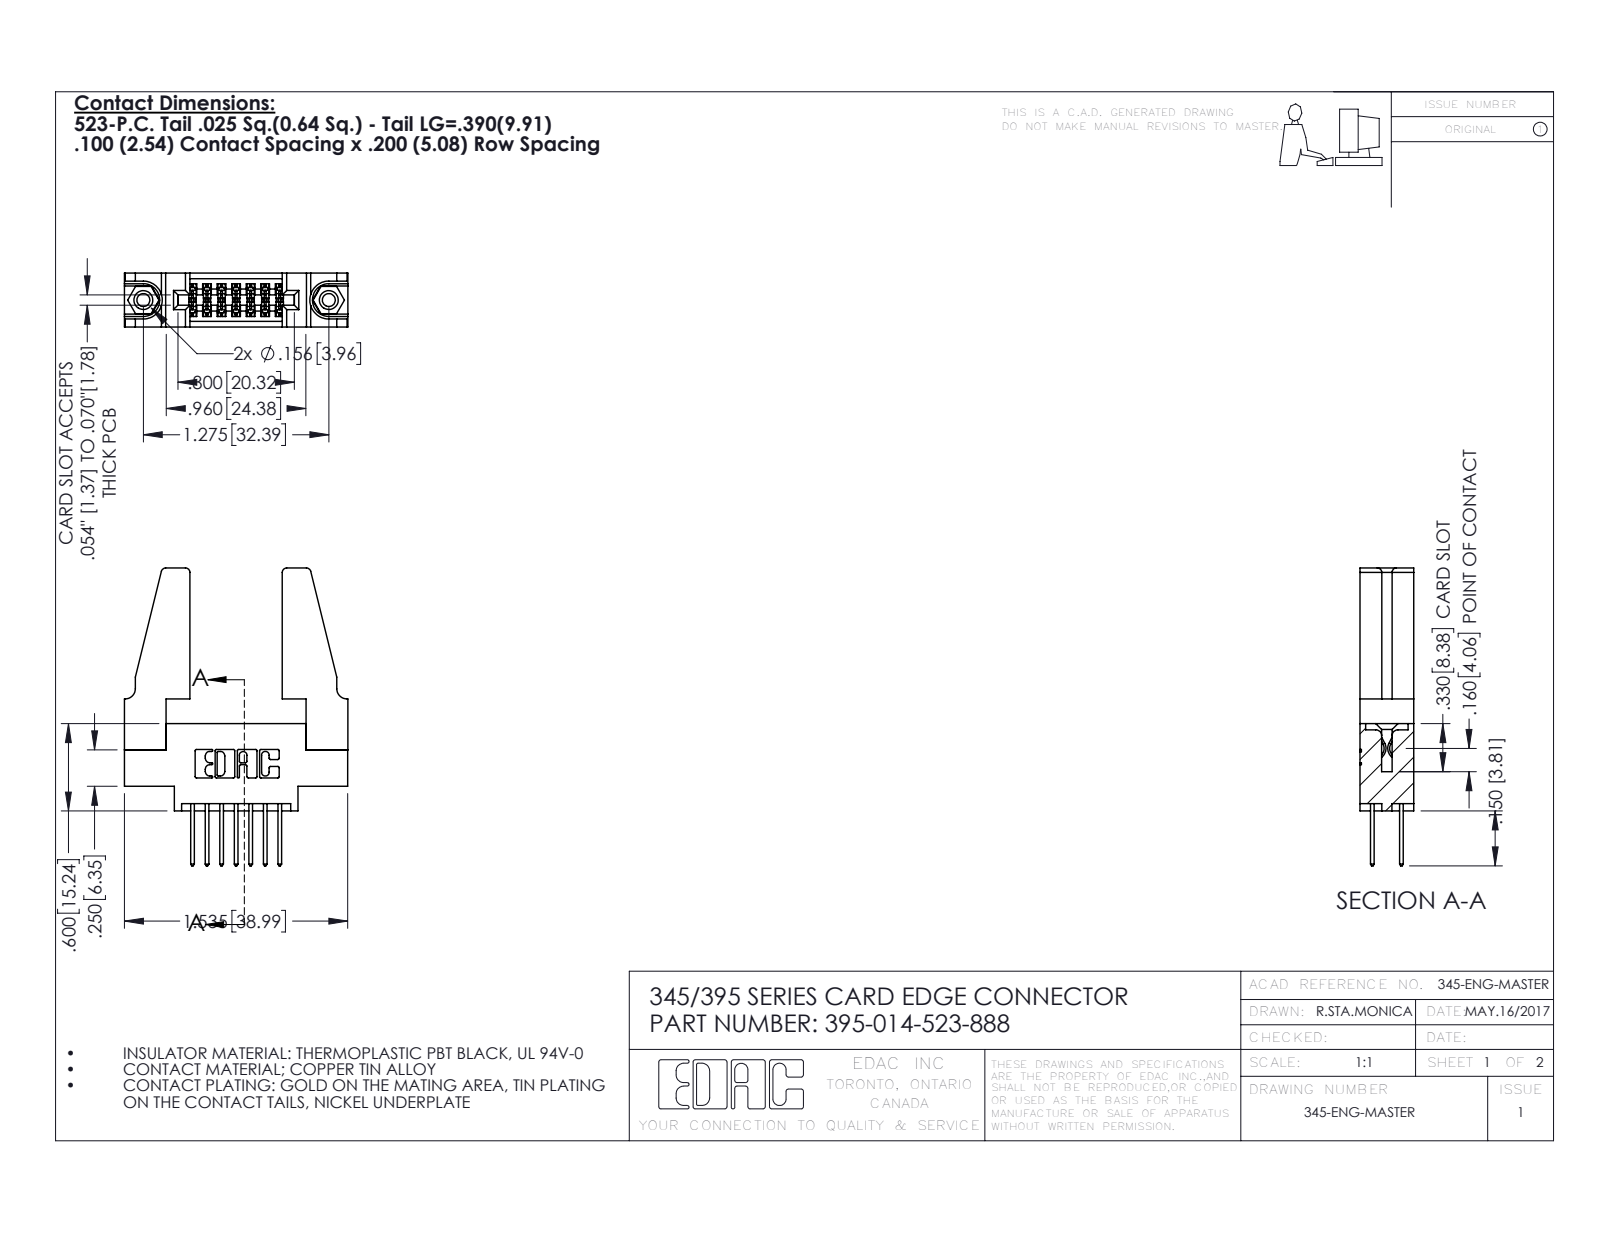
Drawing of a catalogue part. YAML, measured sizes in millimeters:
part_name: "395-014-523-888; 345-250-001_345-250-001-102; 345 Part_0.170 Offset - 0.156 Dia-TH; 345-220-078_345-220-088 (+1 more)"
step_written_by: "SolidWorks 2016 (CONFIG_CONTROL_DESIGN)"
units: millimeters
bodies: {solids: 19, faces: 954, planar: 618, cylindrical: 320, other: 16}
overall_size: [52, 39, 9.4]
volume: 6640
surface_area: 7716
round_holes:
  - {diameter: 2.3, count: 2}
  - {diameter: 3.2, count: 2}
  - {diameter: 4, count: 2}
  - {diameter: 1.6, count: 1}
round_bosses_or_shafts:
  - {diameter: 3.9, count: 2}
partial_cylinders:
  - {radius: 0.3, count: 22}
  - {radius: 0.2, count: 21}
  - {radius: 0.3, count: 14}
  - {radius: 0.8, count: 8}
  - {radius: 0.2, count: 6}
  - {radius: 0.8, count: 6}
  - {radius: 0.7, count: 3}
  - {radius: 0.4, count: 2}
face_to_face_distances: [9.4, 1.8, 7.6, 5.1, 2.5, 6.9, 0.6, 5.7, 3.8, 3.8]
hole_center_spacings: [6.9, 26.5, 32.4]
